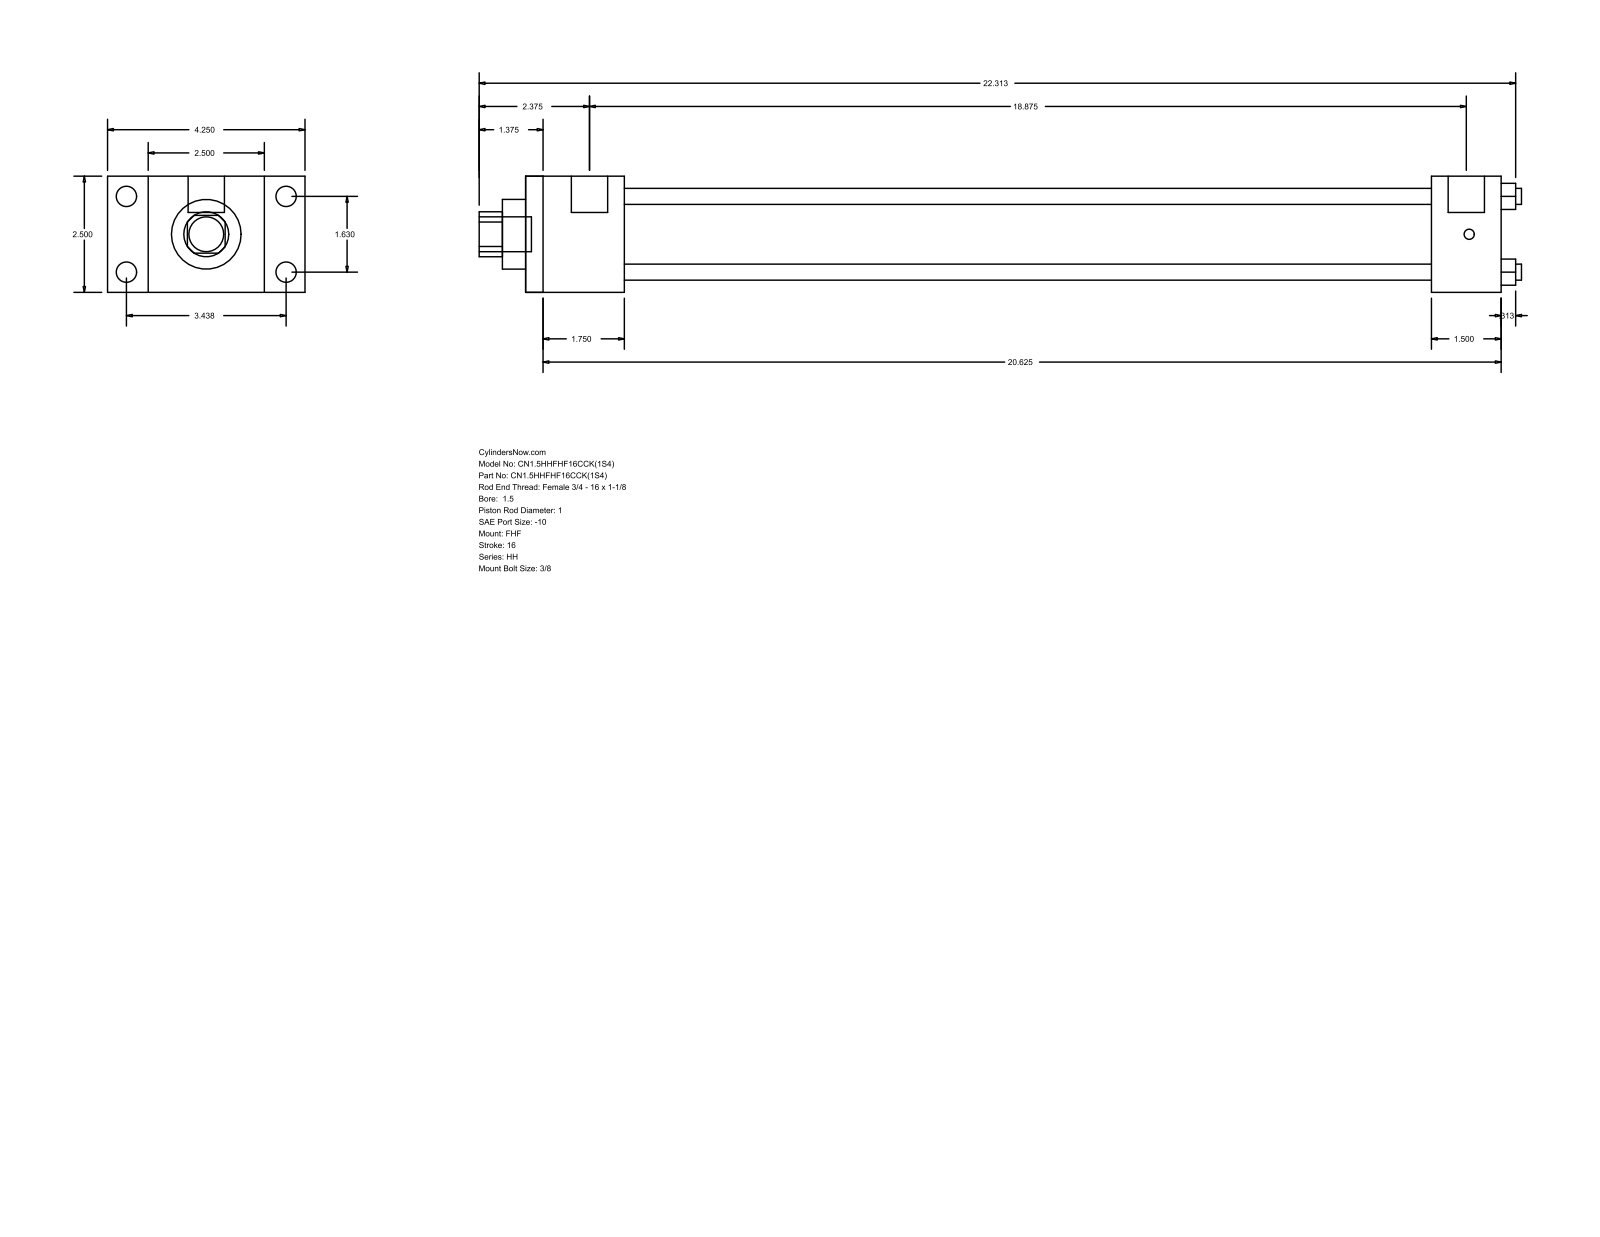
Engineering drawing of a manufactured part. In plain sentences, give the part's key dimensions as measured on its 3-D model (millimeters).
The part is named "HH_FHF__0150_1". Its 3-D file was written by "GSSL Pune (CONFIG_CONTROL_DESIGN)". It is 0 solids with 88 faces: 60 planar, 28 cylindrical and 0 other. Overall it measures 569.91 by 107.95 by 63.5 millimeters. Round holes: 4 of diameter 8.76, 1 of diameter 25.4, 1 of diameter 38.1, 1 of diameter 44.45. Round bosses or shafts: 4 of diameter 11.13, 4 of diameter 5.56, 2 of diameter 19.84, 1 of diameter 19.05. Partial cylindrical surfaces (rounded edges, fillets, slot ends): 1 of radius 12.29. The main face-to-face distances are 63.5, 22.23, 85.73, 53.98, 107.96, 533.4, 479.42, 495.3, 441.32, 38.1. The hole center spacings are 29.27, 41.4, 58.55.
